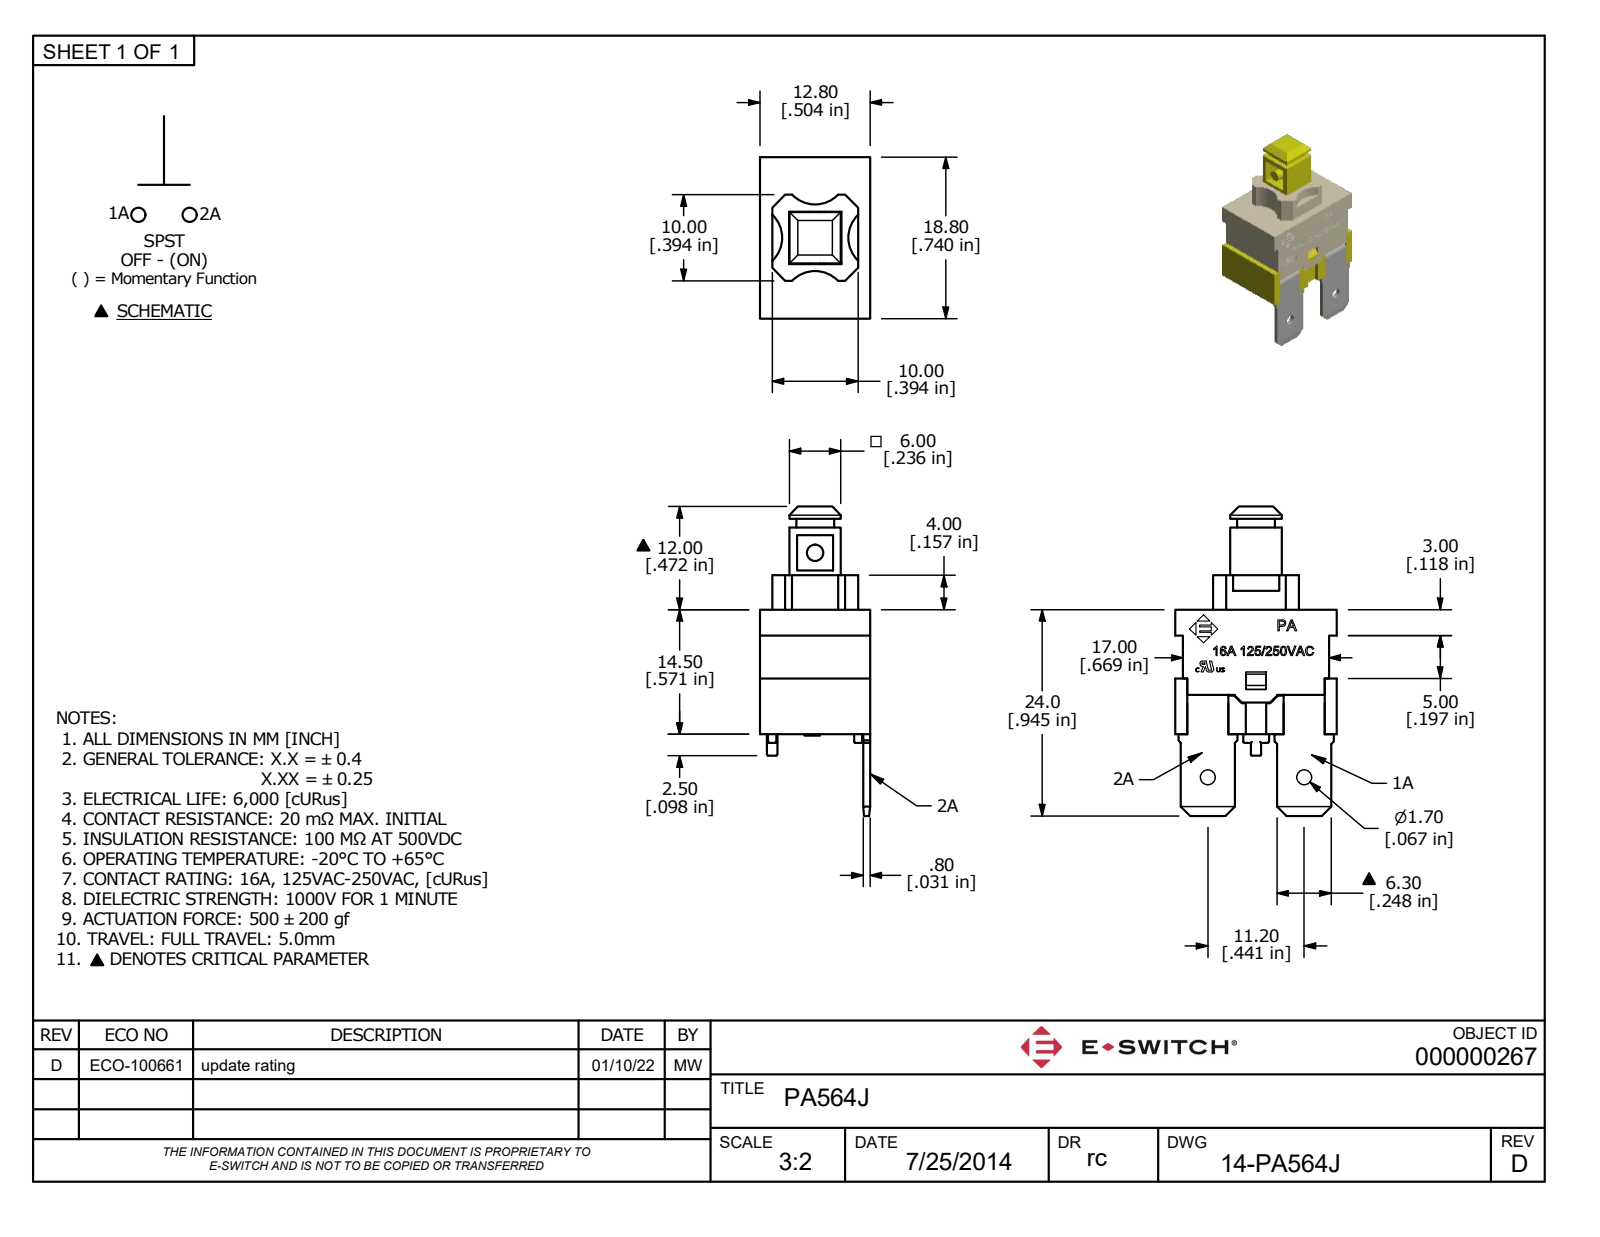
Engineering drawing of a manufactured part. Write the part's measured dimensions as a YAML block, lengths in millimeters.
part_name: "PA564J"
step_written_by: "Autodesk Inventor 2022 (AUTOMOTIVE_DESIGN)"
units: millimeters
bodies: {solids: 1, faces: 769, planar: 572, cylindrical: 67, other: 130}
overall_size: [36, 18.8, 12.8]
volume: 2186
surface_area: 4422
round_holes:
  - {diameter: 1.7, count: 2}
  - {diameter: 3, count: 1}
round_bosses_or_shafts:
  - {diameter: 0.95, count: 4}
  - {diameter: 2.5, count: 1}
  - {diameter: 1.9, count: 1}
partial_cylinders:
  - {radius: 0.25, count: 18}
  - {radius: 0.12, count: 16}
  - {radius: 0.15, count: 8}
  - {radius: 3.71, count: 4}
  - {radius: 1, count: 2}
  - {radius: 0.5, count: 1}
  - {radius: 1.79, count: 1}
  - {radius: 2.32, count: 1}
face_to_face_distances: [0.8, 12, 0.9, 2, 16.8, 8.6, 4.4, 1.1, 12.8, 5.15]
hole_center_spacings: [11.2]
